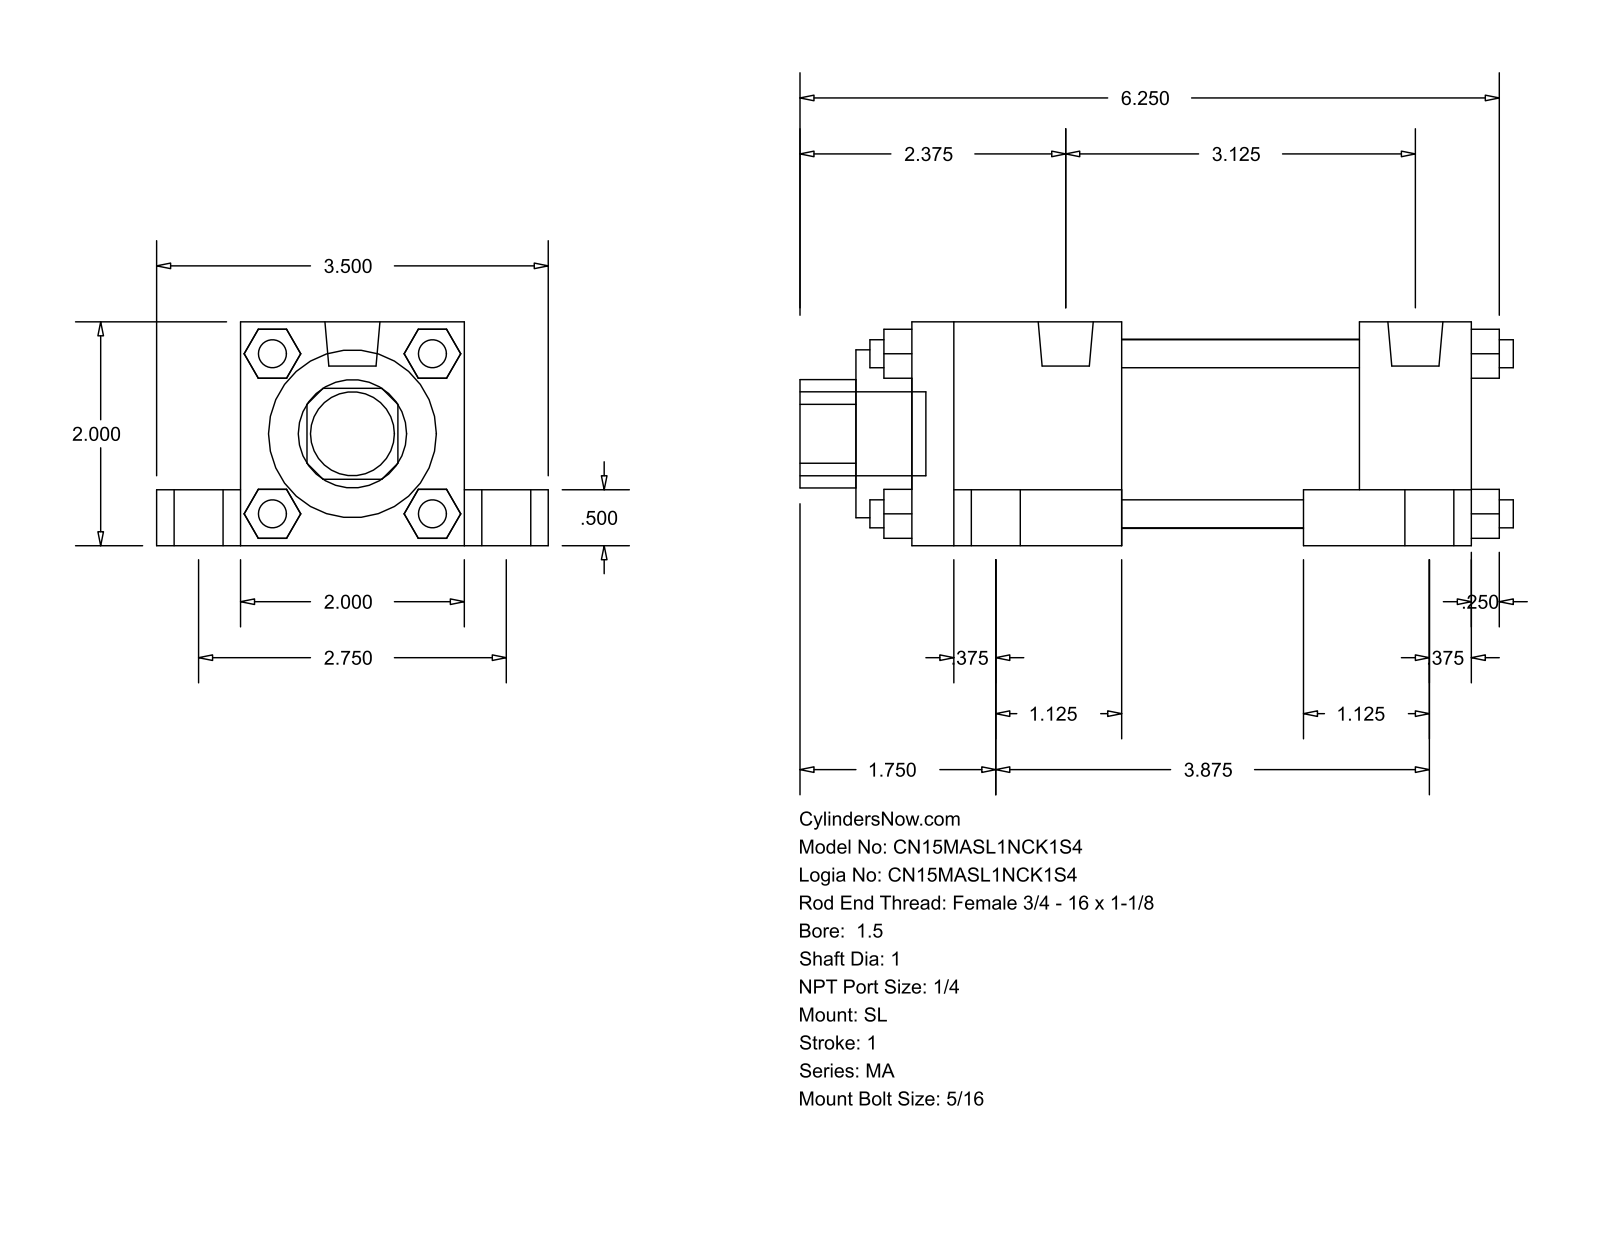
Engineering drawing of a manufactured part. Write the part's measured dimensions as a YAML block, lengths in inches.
part_name: "MA_SL__0150_1"
step_written_by: "GSSL Pune (CONFIG_CONTROL_DESIGN)"
units: inches
bodies: {solids: 0, faces: 148, planar: 112, cylindrical: 36, other: 0}
overall_size: [6.375, 3.5, 2]
round_holes:
  - {diameter: 1, count: 1}
  - {diameter: 1.5, count: 1}
  - {diameter: 1.69, count: 1}
round_bosses_or_shafts:
  - {diameter: 0.687, count: 4}
  - {diameter: 0.437, count: 4}
  - {diameter: 0.313, count: 4}
  - {diameter: 0.25, count: 4}
  - {diameter: 0.492, count: 2}
  - {diameter: 0.75, count: 1}
partial_cylinders:
  - {radius: 0.484, count: 1}
face_to_face_distances: [2, 0.5, 0.75, 2.75, 0.375, 1.5, 0.25, 5, 1, 4]
